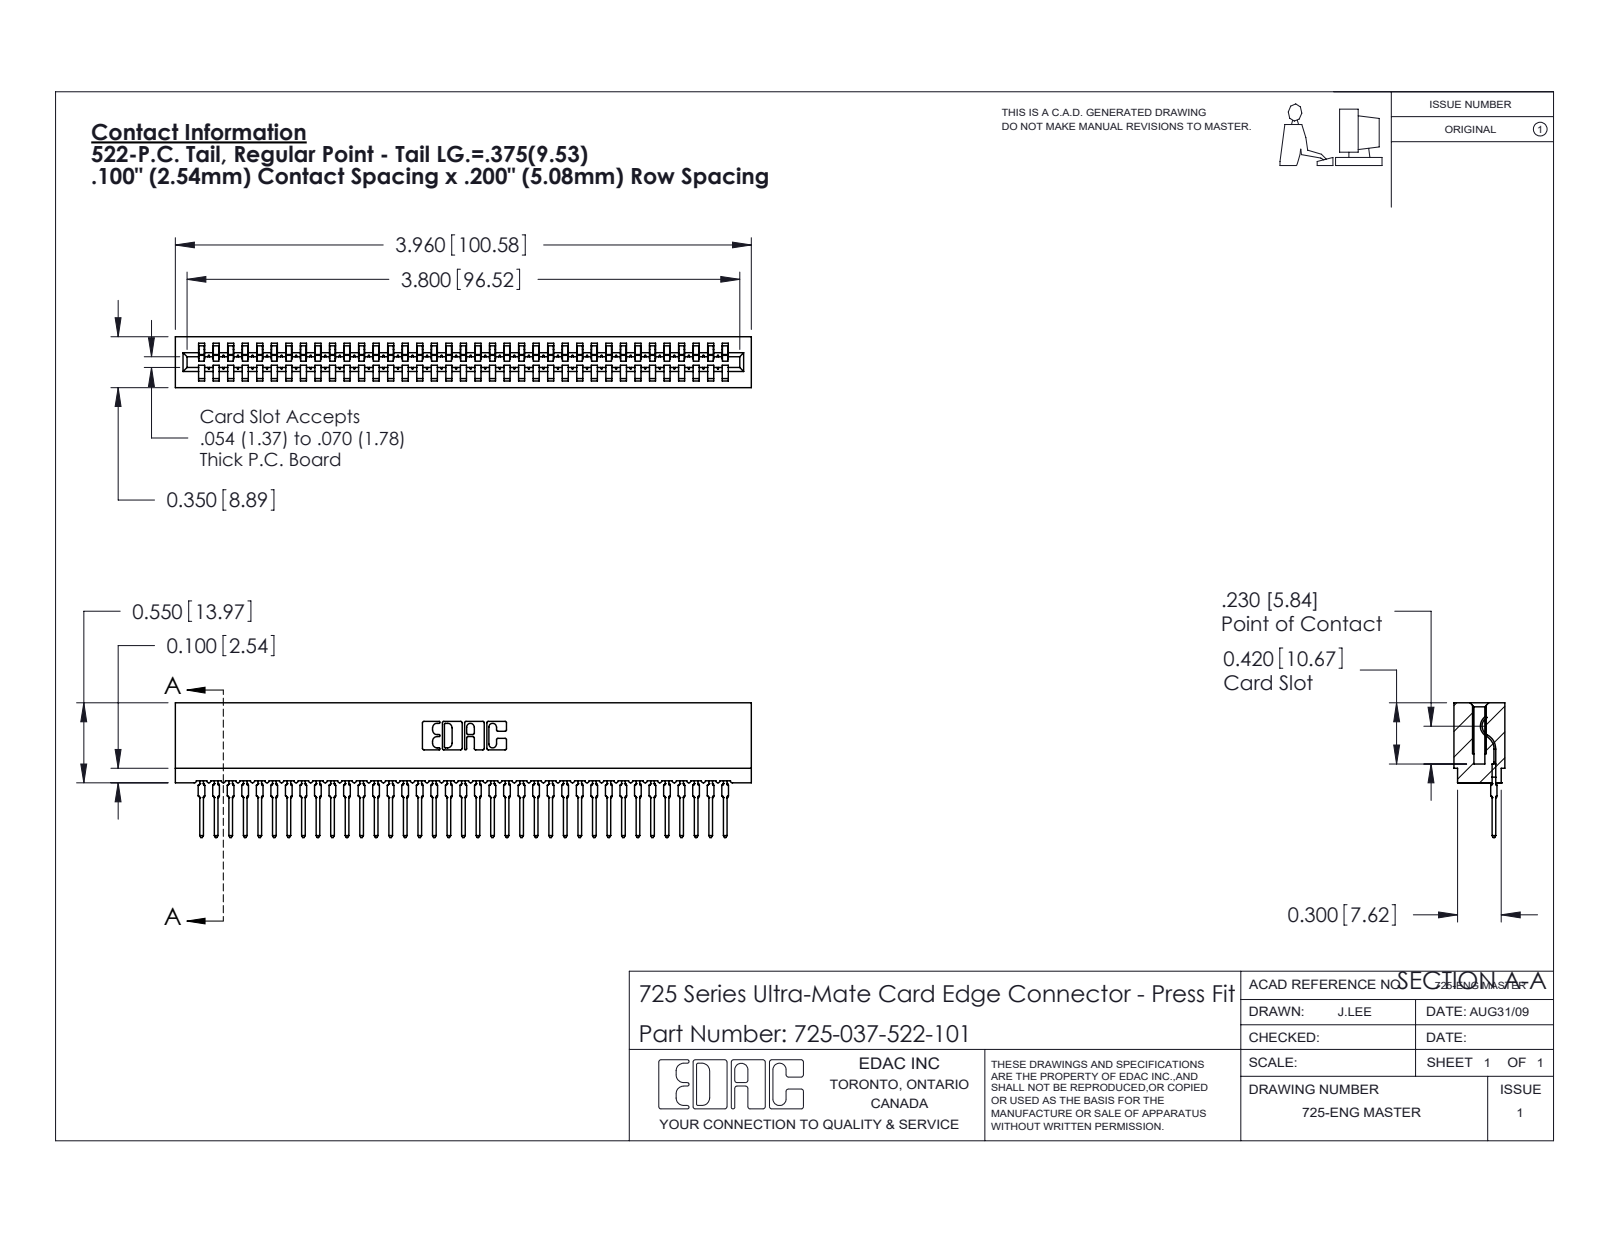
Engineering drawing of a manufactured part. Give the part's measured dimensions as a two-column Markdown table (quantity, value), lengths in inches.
| quantity | value |
| --- | --- |
| part name | 725-037-522-101; 725 Part_Insulator Option - 01; 745-292-001_522 |
| STEP written by | SolidWorks 2020 (CONFIG_CONTROL_DESIGN) |
| units | inches |
| bodies | 38 solids, 4239 faces (2534 planar, 743 cylindrical, 962 other) |
| overall size | 3.96 × 0.926 × 0.35 |
| volume | 0.469 in³ |
| surface area | 22.92 in² |
| partial cylindrical surfaces (radius × count) | 0.015 × 74, 0.021 × 74, 0.01 × 22, 0.007 × 6, 0.031 × 6, 0.005 × 4, 0.011 × 4, 0.026 × 3 |
| main face-to-face distances | 0.35, 0.2, 0.1, 0.212, 0.138, 0.045, 0.305, 0.093, 0.167, 0.063 |
